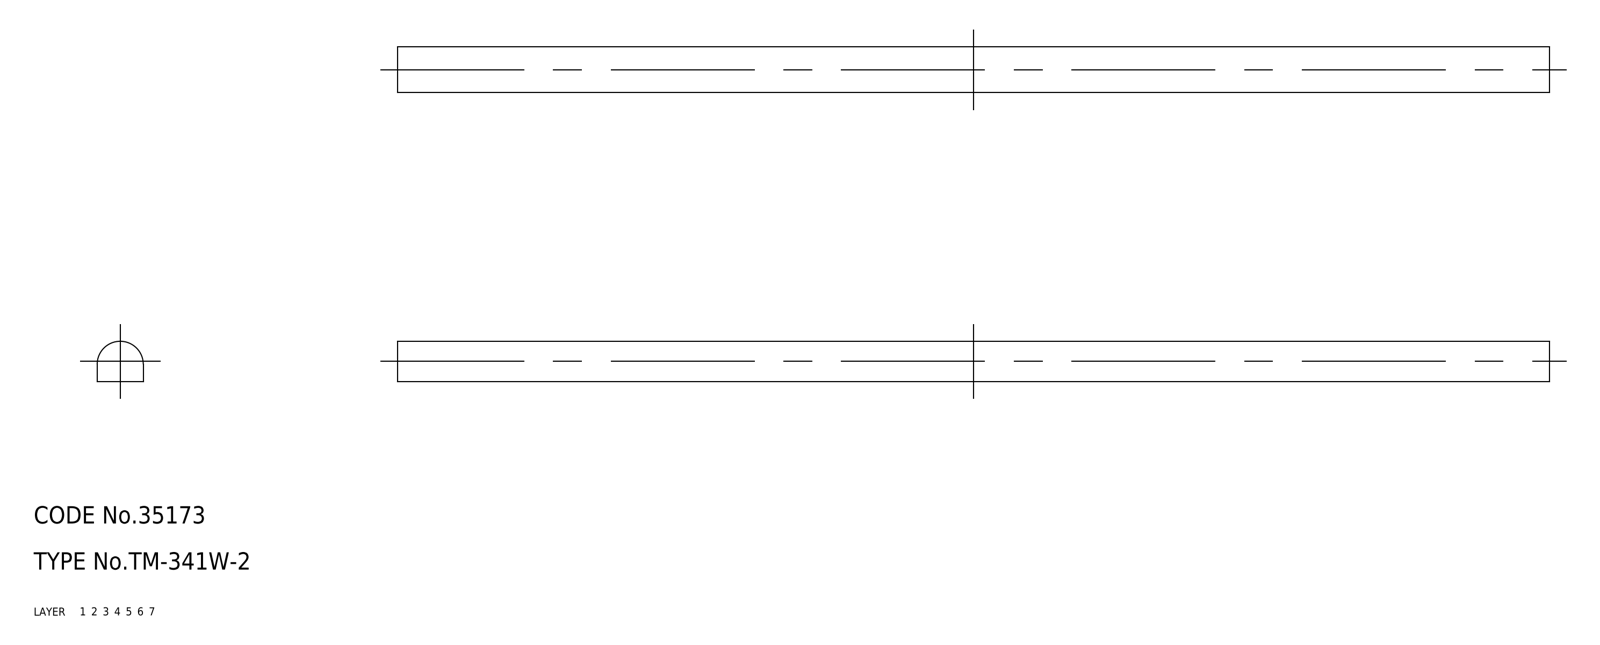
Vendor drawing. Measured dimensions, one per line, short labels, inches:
name: rubber foam; TM_341W_2
written by: SolidWorks 2015 (AUTOMOTIVE_DESIGN)
unit: in
bodies: 1 solid, 6 faces (5 planar, 1 cylindrical, 0 other)
size: 7.874 × 0.315 × 0.276
volume: 0.6 in³; area: 8.389 in²
rounds: 1× R0.157
face distances: 0.315, 7.874
